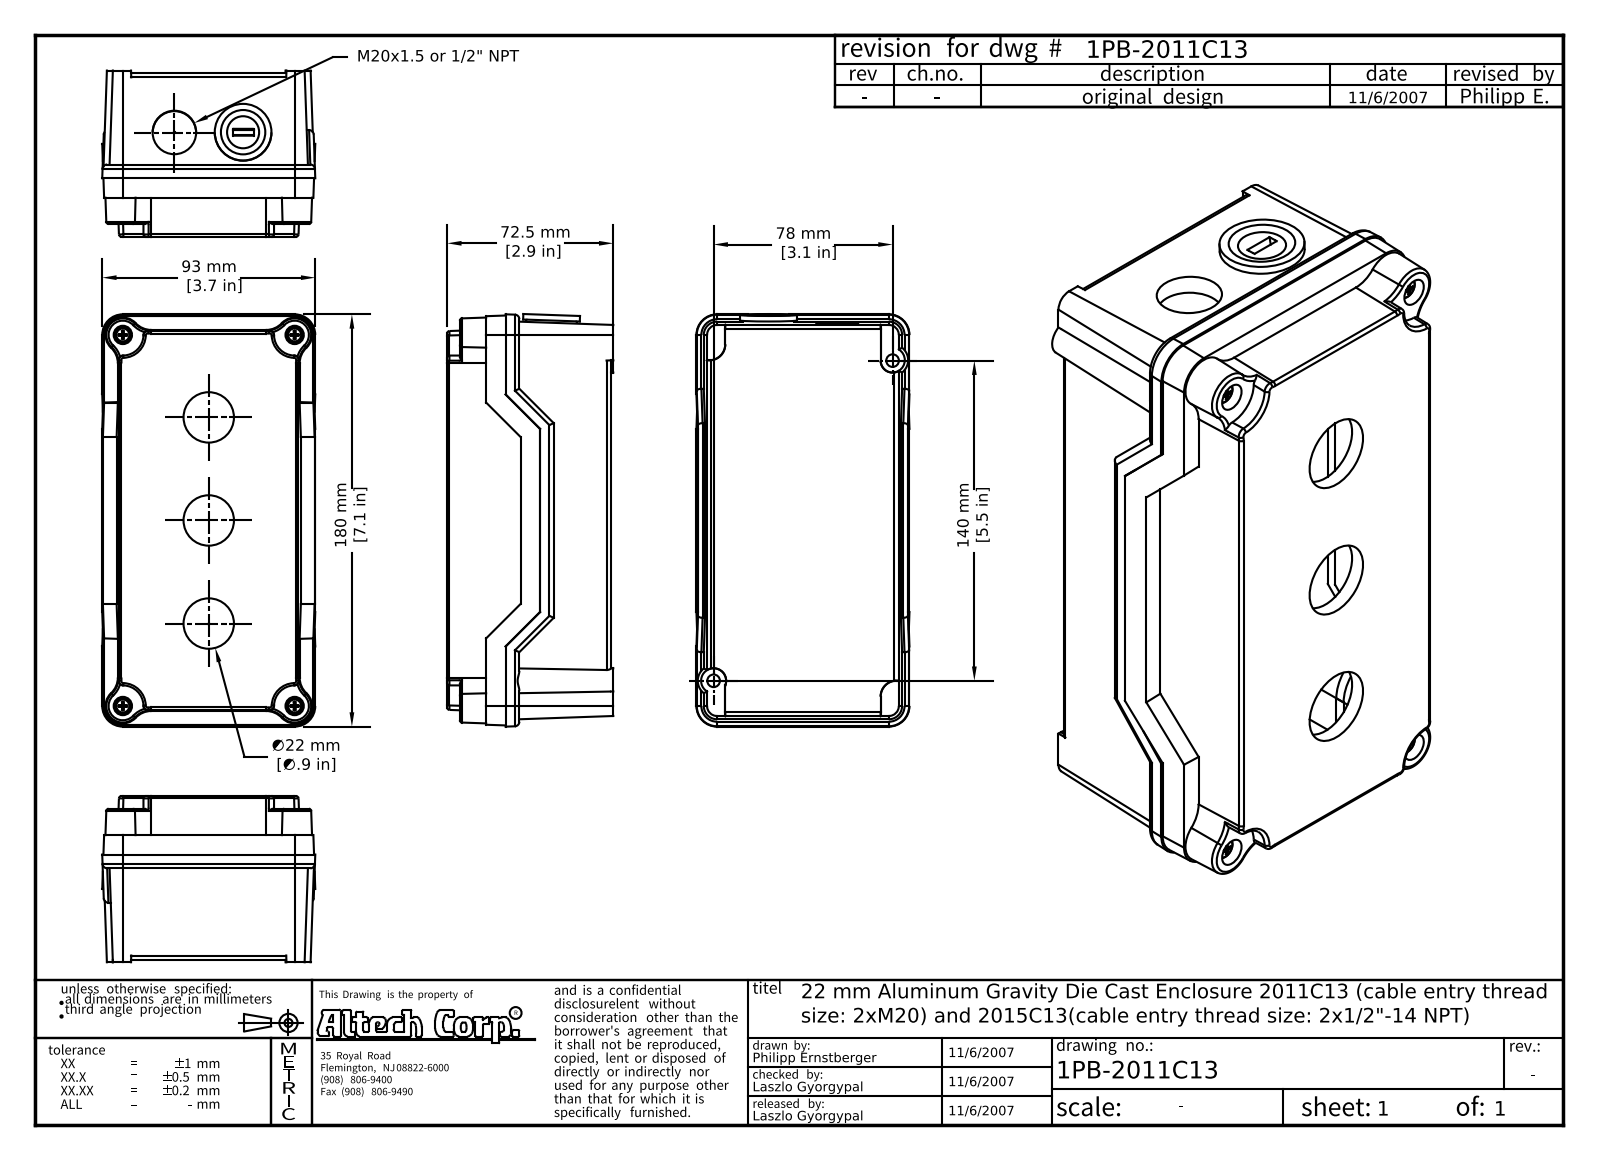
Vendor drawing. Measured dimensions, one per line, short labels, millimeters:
name: 2009E13; enclosure_back; enclosure_front; ISO 7045 Z M4 x 5 - 4.8 - Z (+4 more)
written by: Autodesk Inventor 2008 (AUTOMOTIVE_DESIGN)
unit: mm
bodies: 12 solids, 508 faces (206 planar, 69 cylindrical, 233 other)
size: 180.13 × 93 × 72.5
volume: 354 319 mm³; area: 139 582 mm²
holes: 4× ⌀3.5, 3× ⌀22, 2× ⌀4.3, 2× ⌀19
bosses: 4× ⌀3.18, 2× ⌀9, 2× ⌀4, 2× ⌀3.62, 1× ⌀24.75
rounds: 14× R2, 6× R9, 4× R1, 3× R12, 2× R6, 2× R8.5, 2× R11.5, 1× R7.75
face distances: 65.5, 6, 71.5, 67, 4.5, 61, 74, 40, 21, 46
hole spacings: 51.98, 89.26, 131.46, 30.51, 33.51, 45, 60.59, 75
